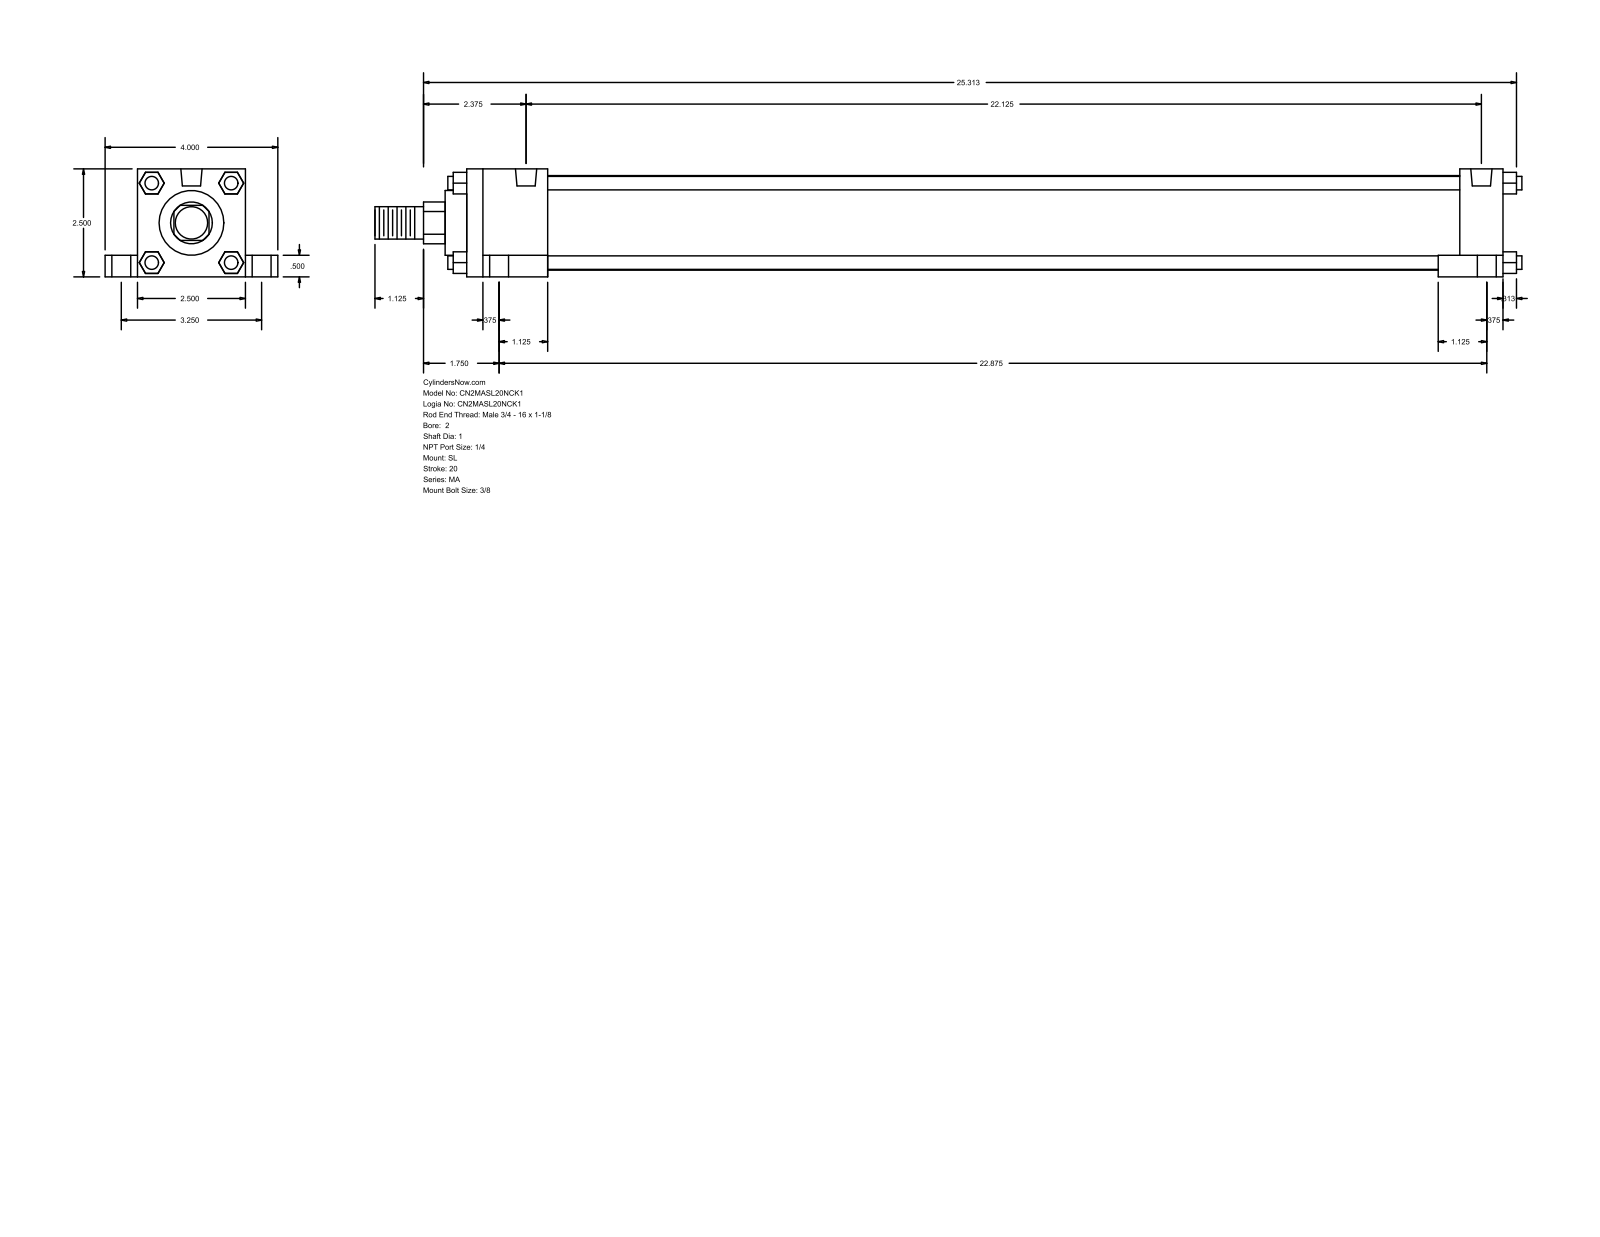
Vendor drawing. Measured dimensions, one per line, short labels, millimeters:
name: MA_SL__0200_1
written by: GSSL Pune (CONFIG_CONTROL_DESIGN)
unit: mm
bodies: 0 solids, 148 faces (112 planar, 36 cylindrical, 0 other)
size: 674.69 × 101.6 × 63.5
holes: 4× ⌀7.94, 4× ⌀11.11, 4× ⌀17.46, 2× ⌀12.49
bosses: 4× ⌀7.94, 1× ⌀55.63, 1× ⌀38.1, 1× ⌀25.4, 1× ⌀19.05
rounds: 1× R12.29
face distances: 63.5, 12.7, 609.6, 19.05, 82.55, 25.4, 50.8, 47.63, 561.97, 584.2
hole spacings: 41.39, 44.22, 82.54, 561.97, 566.65, 579.32, 581.03, 586.86
